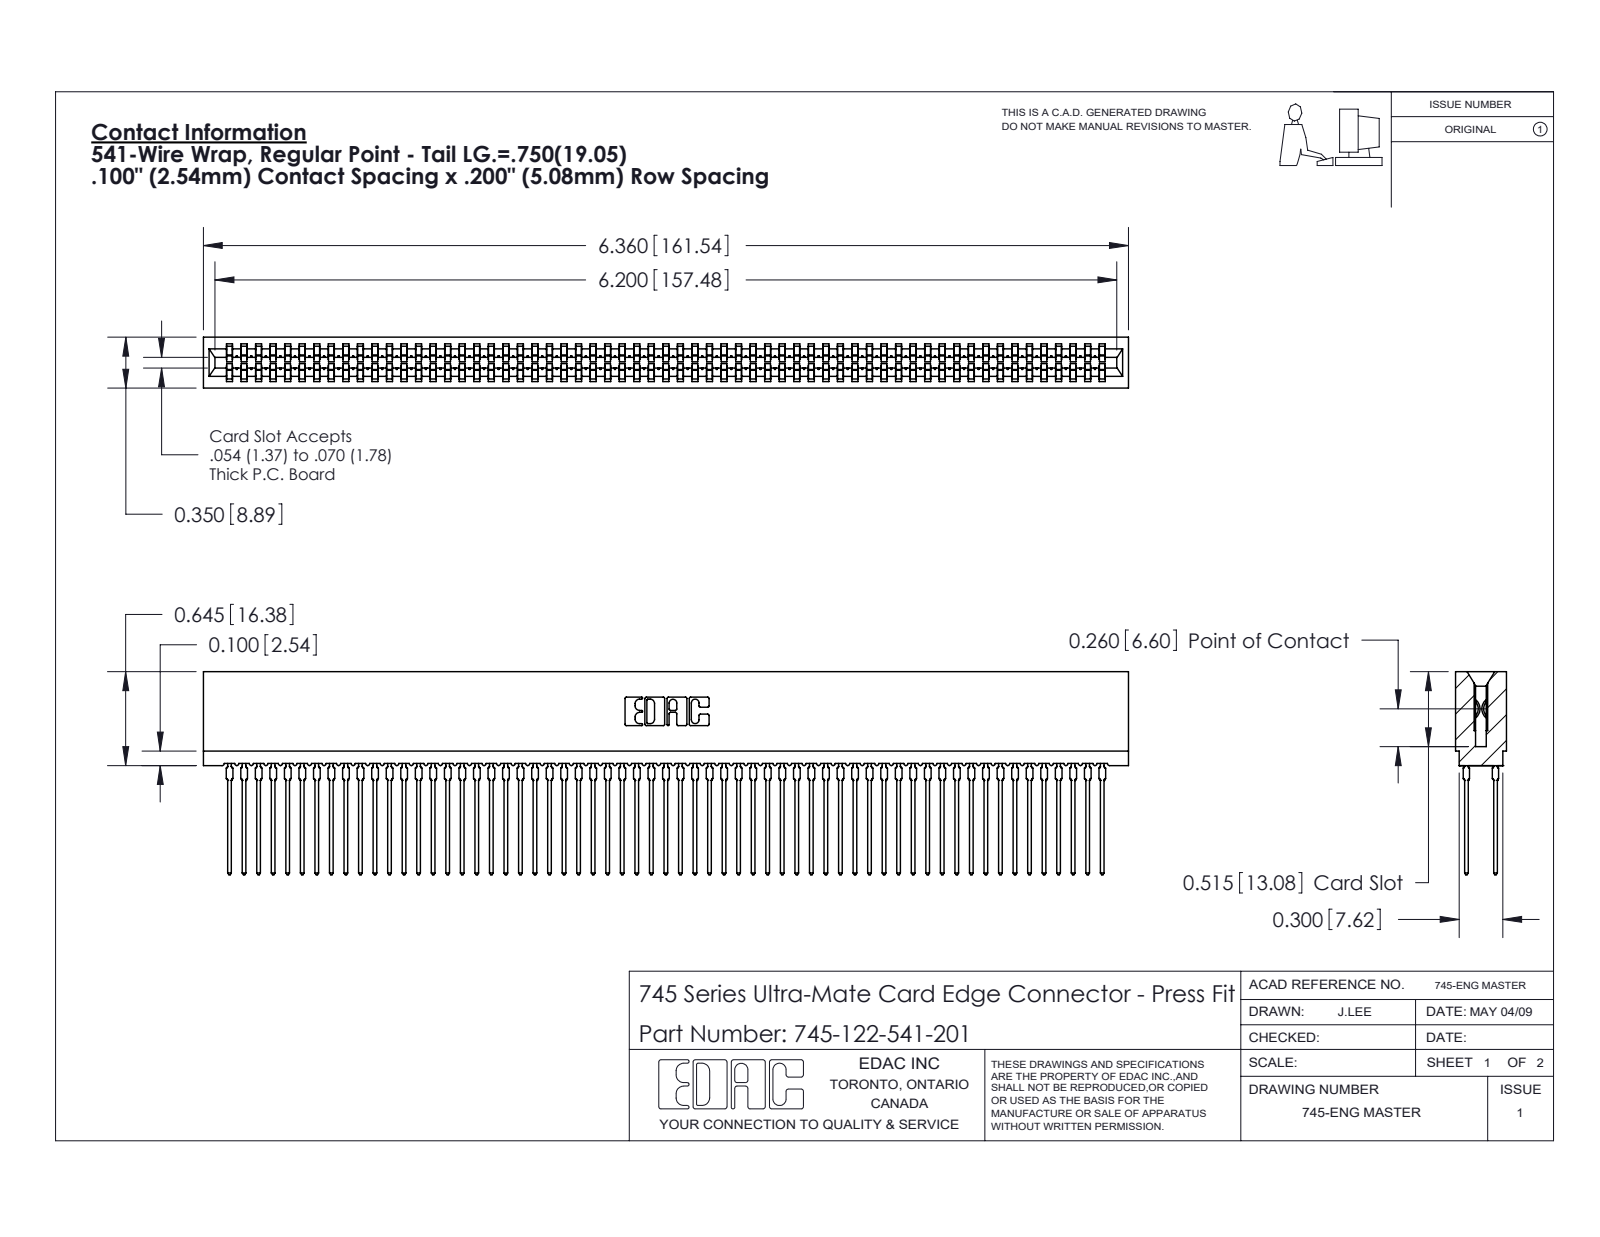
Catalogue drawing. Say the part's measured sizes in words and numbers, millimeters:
The part is named "745-122-541-201; 745 Part_Insulator Option - 01; 745-292-001_541". Its 3-D file was written by "SolidWorks 2020 (CONFIG_CONTROL_DESIGN)". It is 123 solids with 11014 faces: 5667 planar, 2175 cylindrical and 3172 other. Overall it measures 161.5 by 35.5 by 8.9 millimeters. Its volume is 15 000 cubic millimeters and its surface area 33 420 square millimeters. Partial cylindrical surfaces (rounded edges, fillets, slot ends): 244 of radius 0.5, 122 of radius 0.4, 22 of radius 0.3, 8 of radius 0.1, 8 of radius 0.3, 6 of radius 0.2, 6 of radius 0.8, 3 of radius 0.7. The main face-to-face distances are 1.6, 7.3, 5.1, 8.9, 2.2, 6.7, 0.6, 1.1, 7.7, 0.5.
